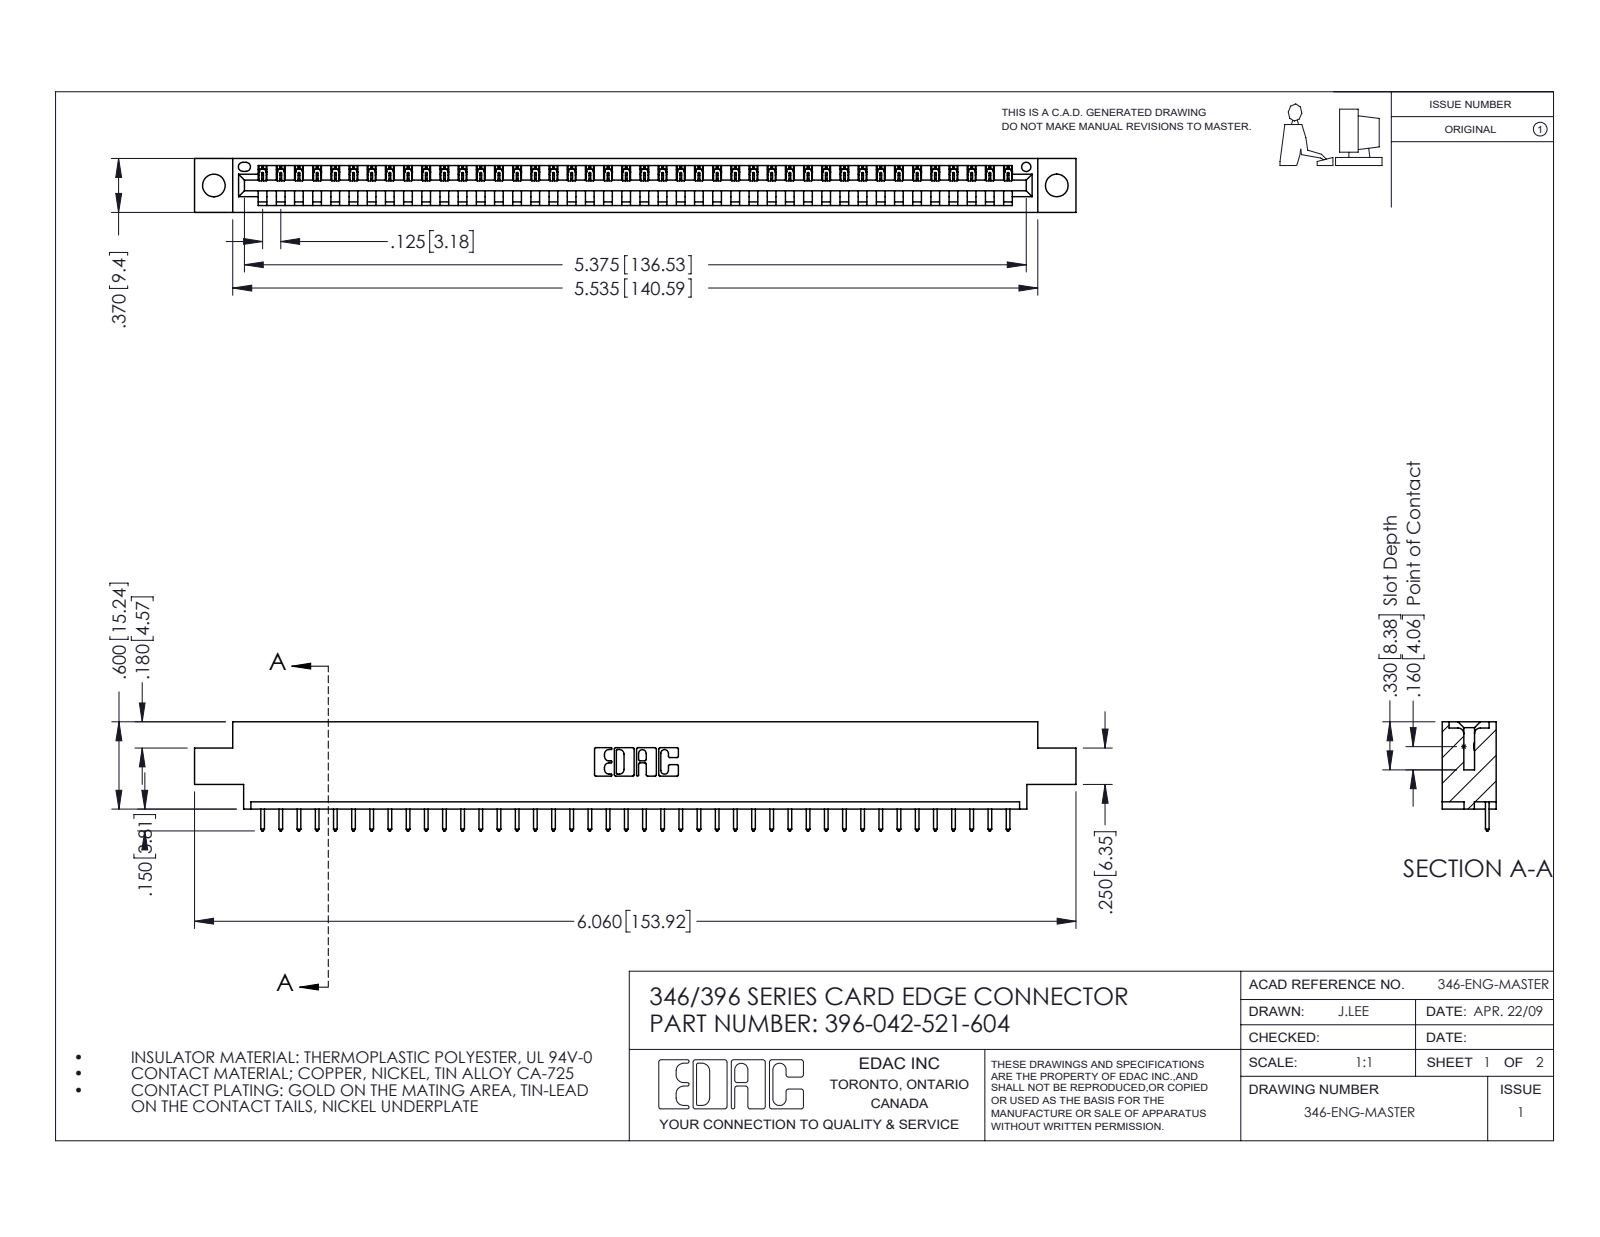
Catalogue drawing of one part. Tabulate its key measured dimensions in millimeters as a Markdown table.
| quantity | value |
| --- | --- |
| part name | 345-292-001_345-293-121; 346 Part_0.170 Offset - 0.156 Dia-TH; 396-042-521-604 |
| STEP written by | SolidWorks 2016 (CONFIG_CONTROL_DESIGN) |
| units | millimeters |
| bodies | 43 solids, 2562 faces (1760 planar, 802 cylindrical, 0 other) |
| overall size | 153.9 × 19.1 × 9.4 |
| volume | 14 400 mm³ |
| surface area | 17 450 mm² |
| round holes (diameter × count) | 4 × 2, 1.6 × 1 |
| partial cylindrical surfaces (radius × count) | 0.2 × 84, 0.3 × 84, 0.3 × 22, 0.2 × 6, 0.8 × 6, 0.7 × 3, 0.8 × 2, 1 × 2 |
| main face-to-face distances | 1.2, 8.2, 9.4, 6.4, 1.8, 7.6, 0.6, 3.8, 5.6, 2.5 |
| hole center spacings | 6.2, 141.9, 147.2 |
